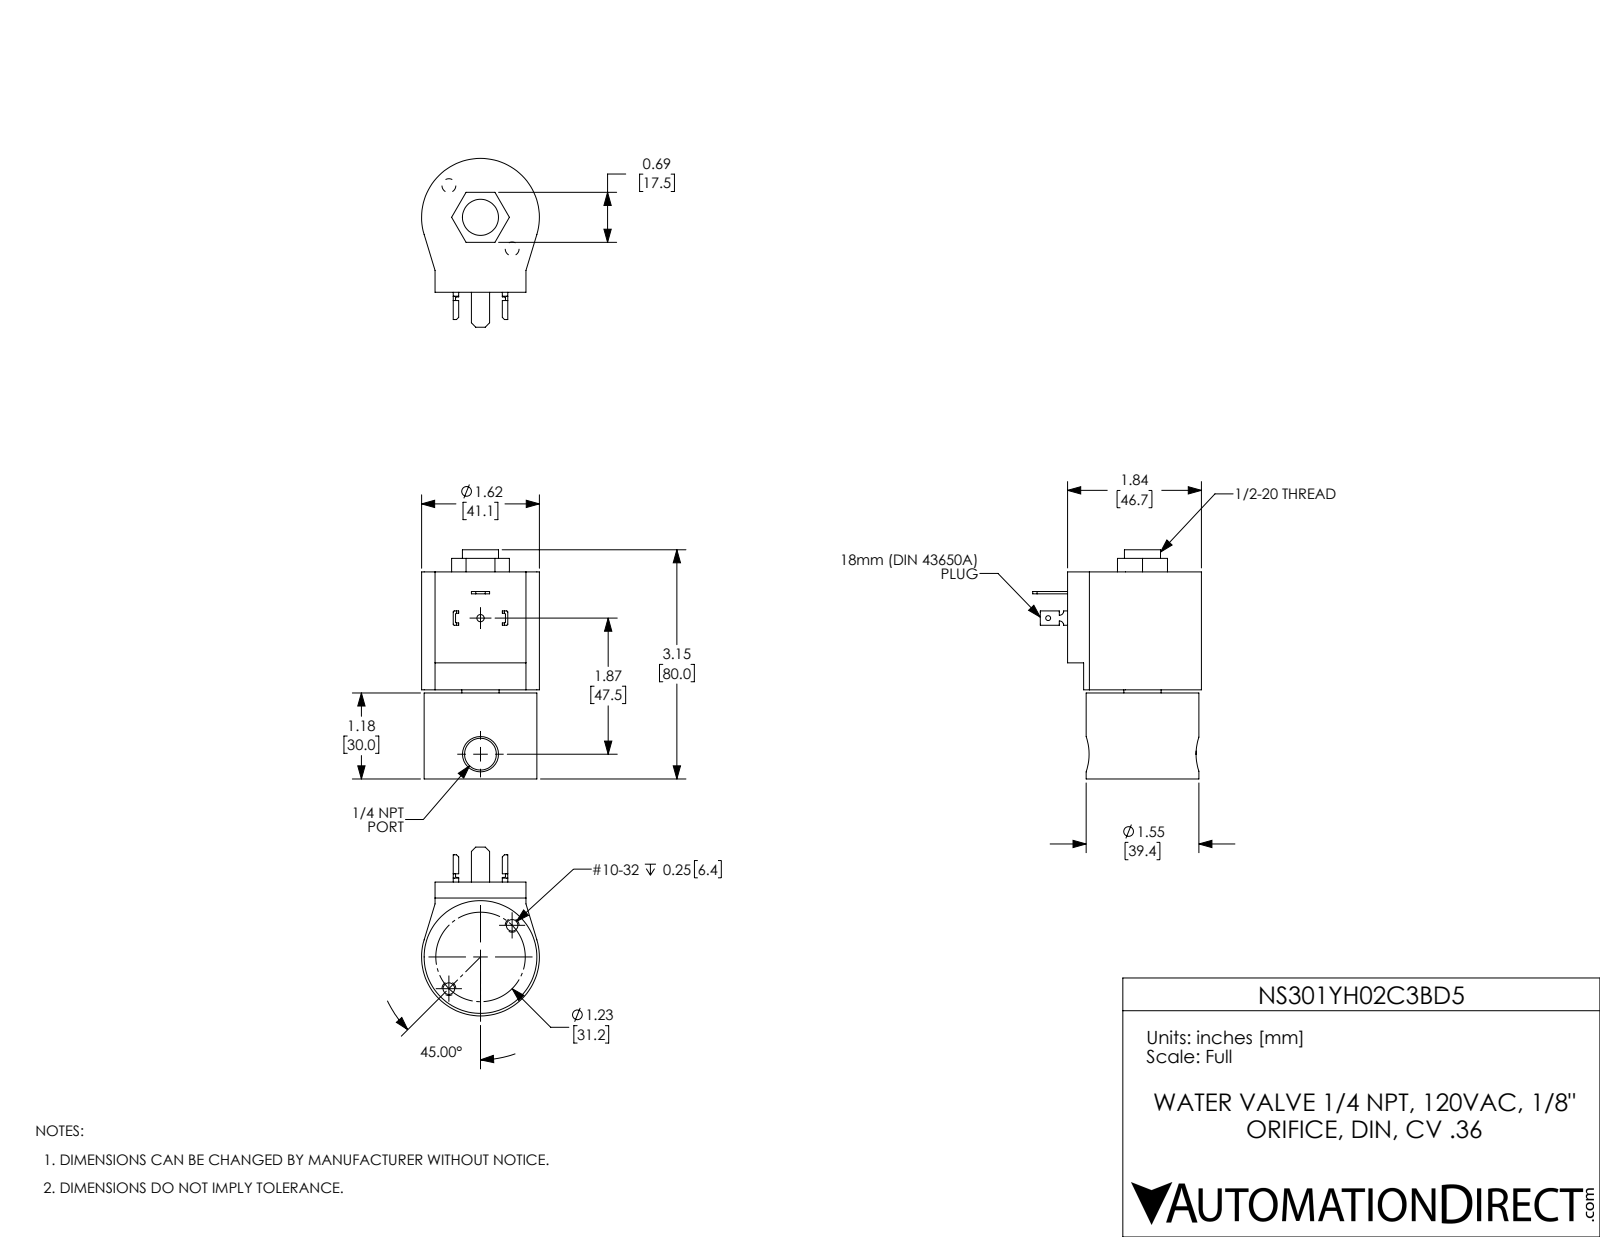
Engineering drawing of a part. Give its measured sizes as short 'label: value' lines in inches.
name: NS301YH02C3BD5
written by: SolidWorks 2024 (CONFIG_CONTROL_DESIGN)
unit: in
bodies: 6 solids, 130 faces (73 planar, 49 cylindrical, 8 other)
size: 3.15 × 2.32 × 1.62
volume: 6.027 in³; area: 33.08 in²
holes: 2× ⌀0.159, 1× ⌀0.067, 1× ⌀0.1, 1× ⌀0.437, 1× ⌀0.496, 1× ⌀0.512, 1× ⌀1.155
bosses: 1× ⌀1.55
rounds: 8× R0.015, 2× R0.06, 1× R0.81
face distances: 2.845, 1.182, 1.663, 1.225, 0.043, 1.62, 1.287, 0.106, 0.062, 1.558
hole spacings: 0.615, 1.23, 1.87
